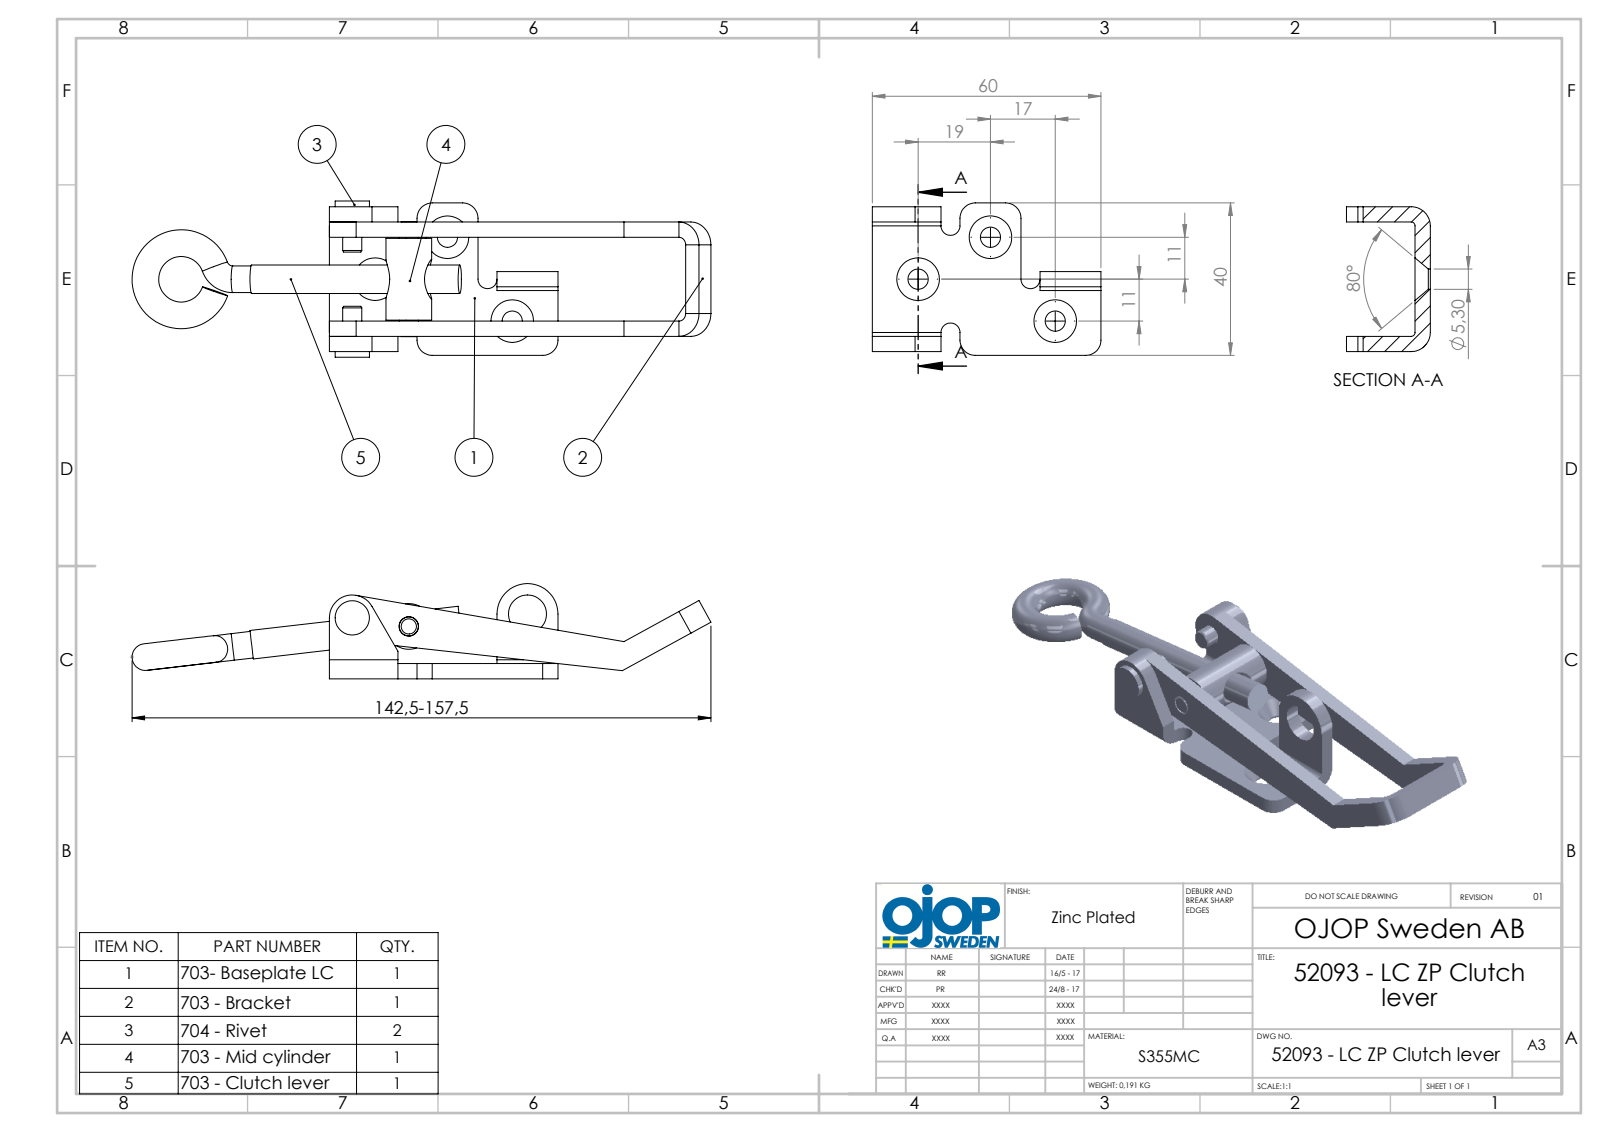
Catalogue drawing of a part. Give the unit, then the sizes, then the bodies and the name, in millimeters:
Units: millimetres
Overall size (bounding box): 151.93 × 41 × 25
Round holes (diameter × count): ⌀5.3 ×3, ⌀5.1 ×2, ⌀7.2 ×1, ⌀7.7 ×1, ⌀10 ×1
Round bosses / shafts (diameter × count): ⌀7 ×2, ⌀5 ×2, ⌀12 ×1, ⌀9 ×1, ⌀7.5 ×1
Partial cylindrical surfaces — rounded edges, fillets, slot ends (radius × count): R4 ×4, R1 ×3, R2.5 ×3, R5 ×3, R6 ×3, R2 ×2, R8 ×1
Main face-to-face distances: 4, 26, 30, 22, 17, 13, 9, 21, 8, 34
Hole centre spacings: 15.02, 21.95, 27.8, 31.32, 37.64, 46.01
Volume: 24 497 mm³ · Surface area: 17 199 mm²
Bodies: 6 solids, 159 faces (65 planar, 68 cylindrical, 26 other)
Part name (STEP PRODUCT): 703 - öglebult m8x60x12; 52093 - LC ZP Clutch lever; 703- Platta LC; 703 - Bygel (+2 more)
STEP written by: SolidWorks 2015 (AUTOMOTIVE_DESIGN)
